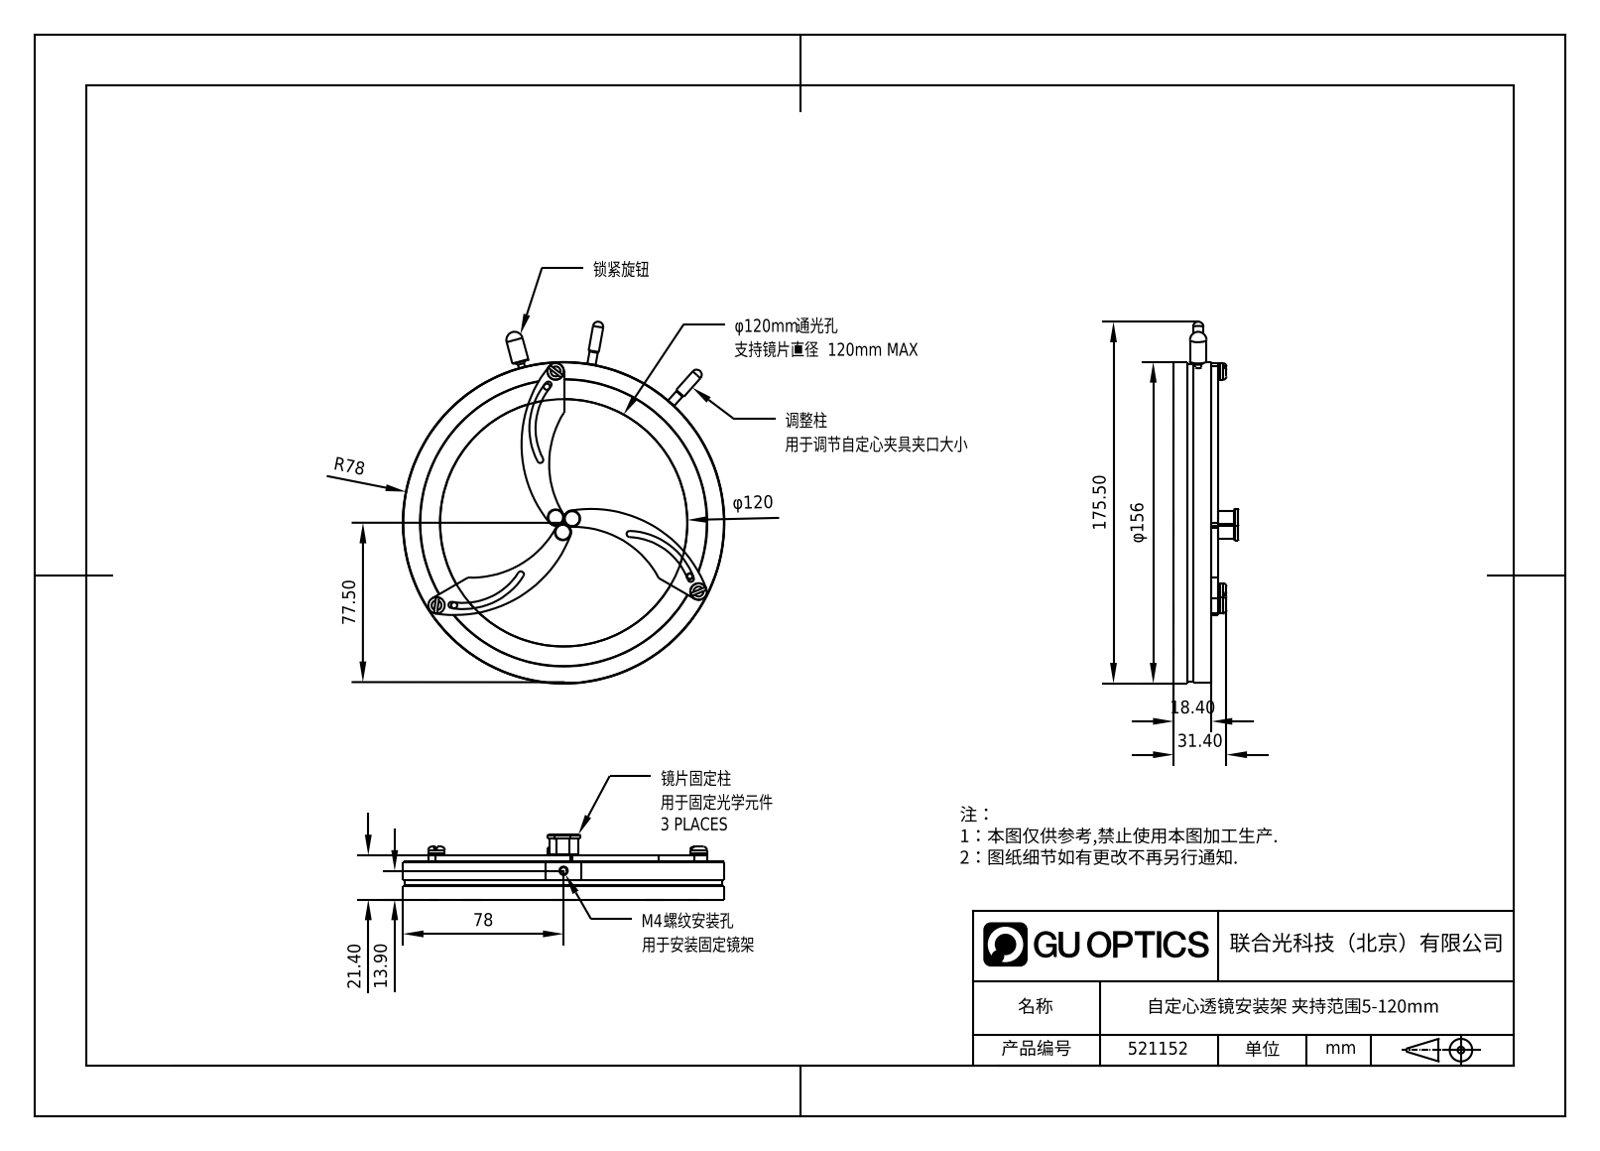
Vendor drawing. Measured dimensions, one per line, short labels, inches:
written by: SolidWorks 2021 (CONFIG_CONTROL_DESIGN)
unit: in
bodies: 0 solids, 380 faces (148 planar, 125 cylindrical, 107 other)
size: 6.911 × 6.142 × 1.248
holes: 8× ⌀0.197, 1× ⌀0.118, 1× ⌀0.13, 1× ⌀4.724, 1× ⌀5.472
bosses: 8× ⌀0.181, 4× ⌀0.315, 3× ⌀0.307, 3× ⌀0.236, 2× ⌀0.197, 2× ⌀0.157, 2× ⌀0.118, 1× ⌀6.142
rounds: 6× R0.059, 3× R0.157, 3× R1.24, 3× R1.358, 3× R1.833, 3× R2.362
face distances: 0.724, 0.134, 0.591, 0.02, 0.705, 0.571, 0.118, 0.843, 0.709, 0.138
hole spacings: 2.48, 4.583, 1.898, 1.898, 3.507, 3.508, 4.961, 0.225
